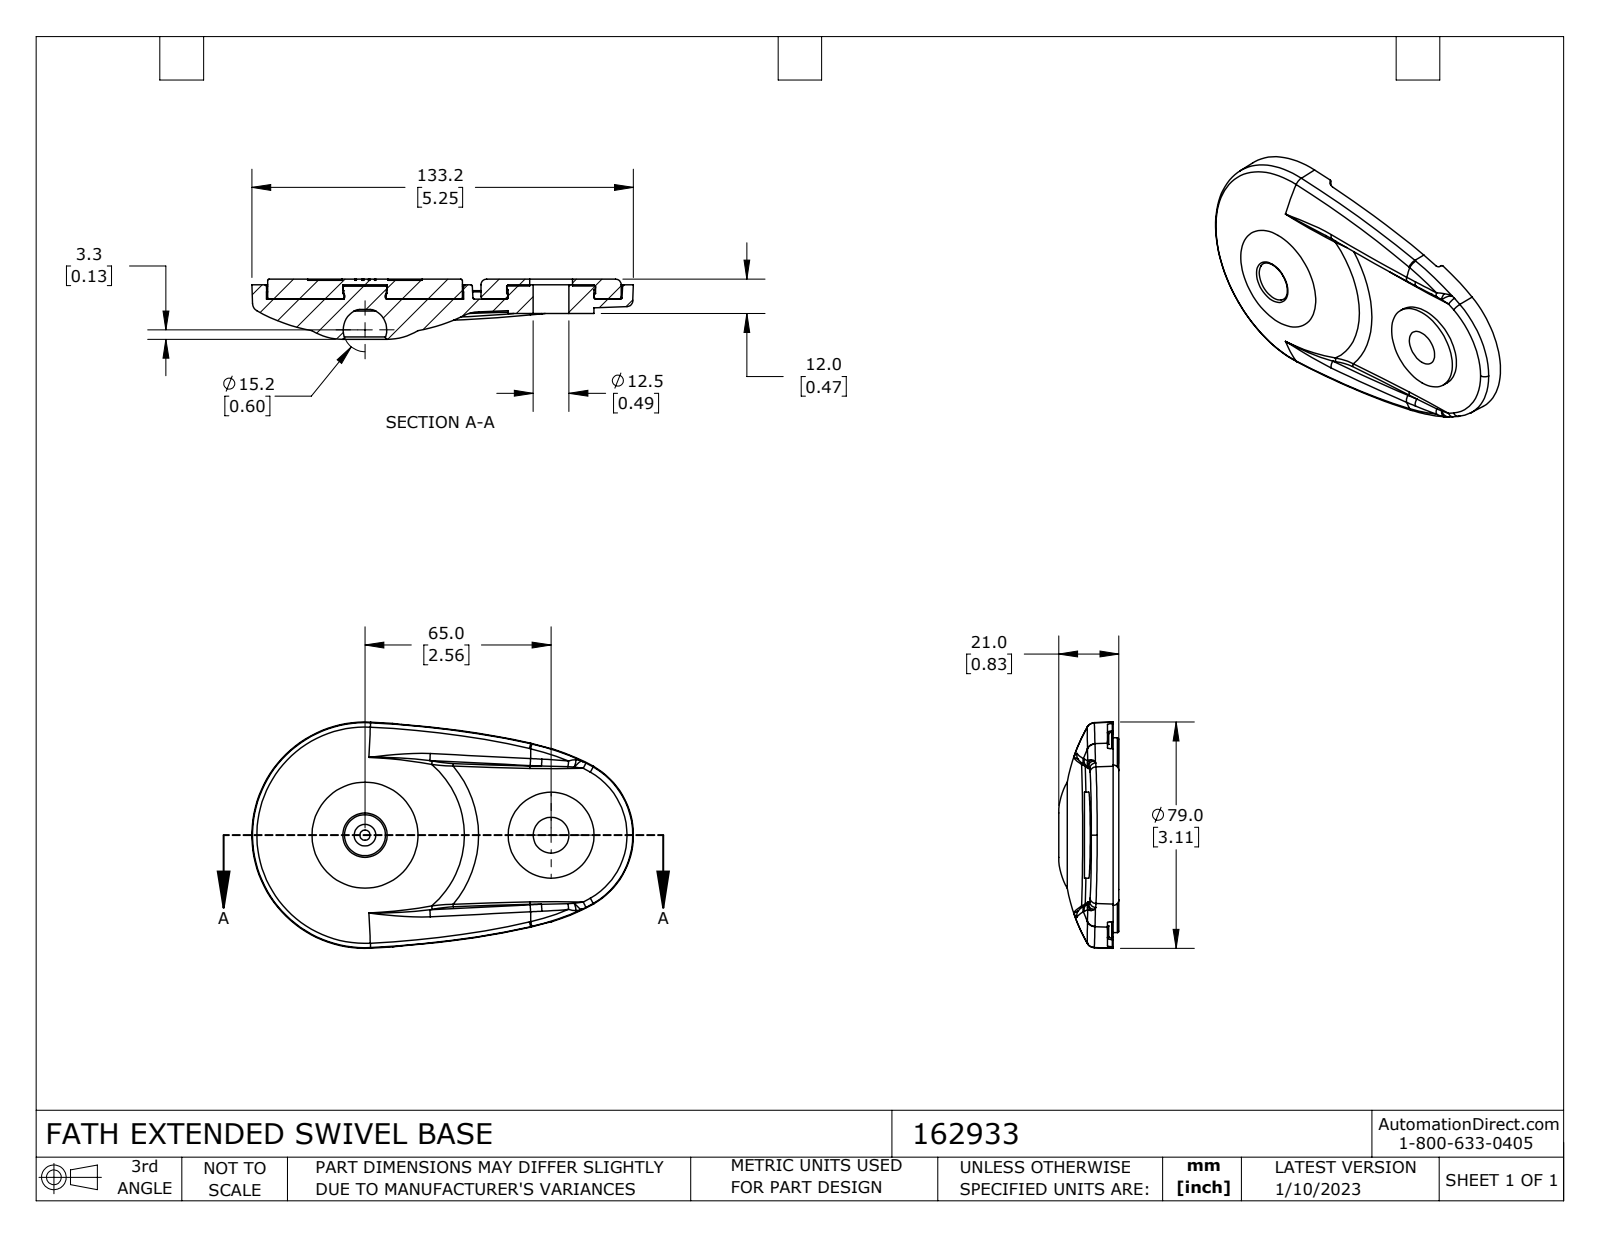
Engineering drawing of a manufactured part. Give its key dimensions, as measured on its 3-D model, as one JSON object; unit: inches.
{"part_name": "162933", "step_written_by": "SolidWorks 2021 (CONFIG_CONTROL_DESIGN)", "units": "inches", "bodies": {"solids": 3, "faces": 252, "planar": 30, "cylindrical": 36, "other": 186}, "overall_size": [5.246, 3.11, 0.827], "volume_in3": 6.016, "surface_area_in2": 58.06, "round_holes": [[0.13, 2], [0.492, 1], [0.591, 1], [0.61, 1], [1.22, 1], [1.575, 1], [2.711, 1]], "round_bosses_or_shafts": [[2.677, 1], [1.929, 1], [1.181, 1], [0.63, 1], [0.583, 1]], "partial_cylinders_radius": [[0.02, 2], [0.039, 1], [0.118, 1]], "face_to_face_distances": [0.276, 0.079, 0.197, 0.016, 0.063, 0.26, 0.472, 0.457, 0.394, 0.094], "hole_center_spacings": [0.669, 2.645, 1.339, 2.559]}
